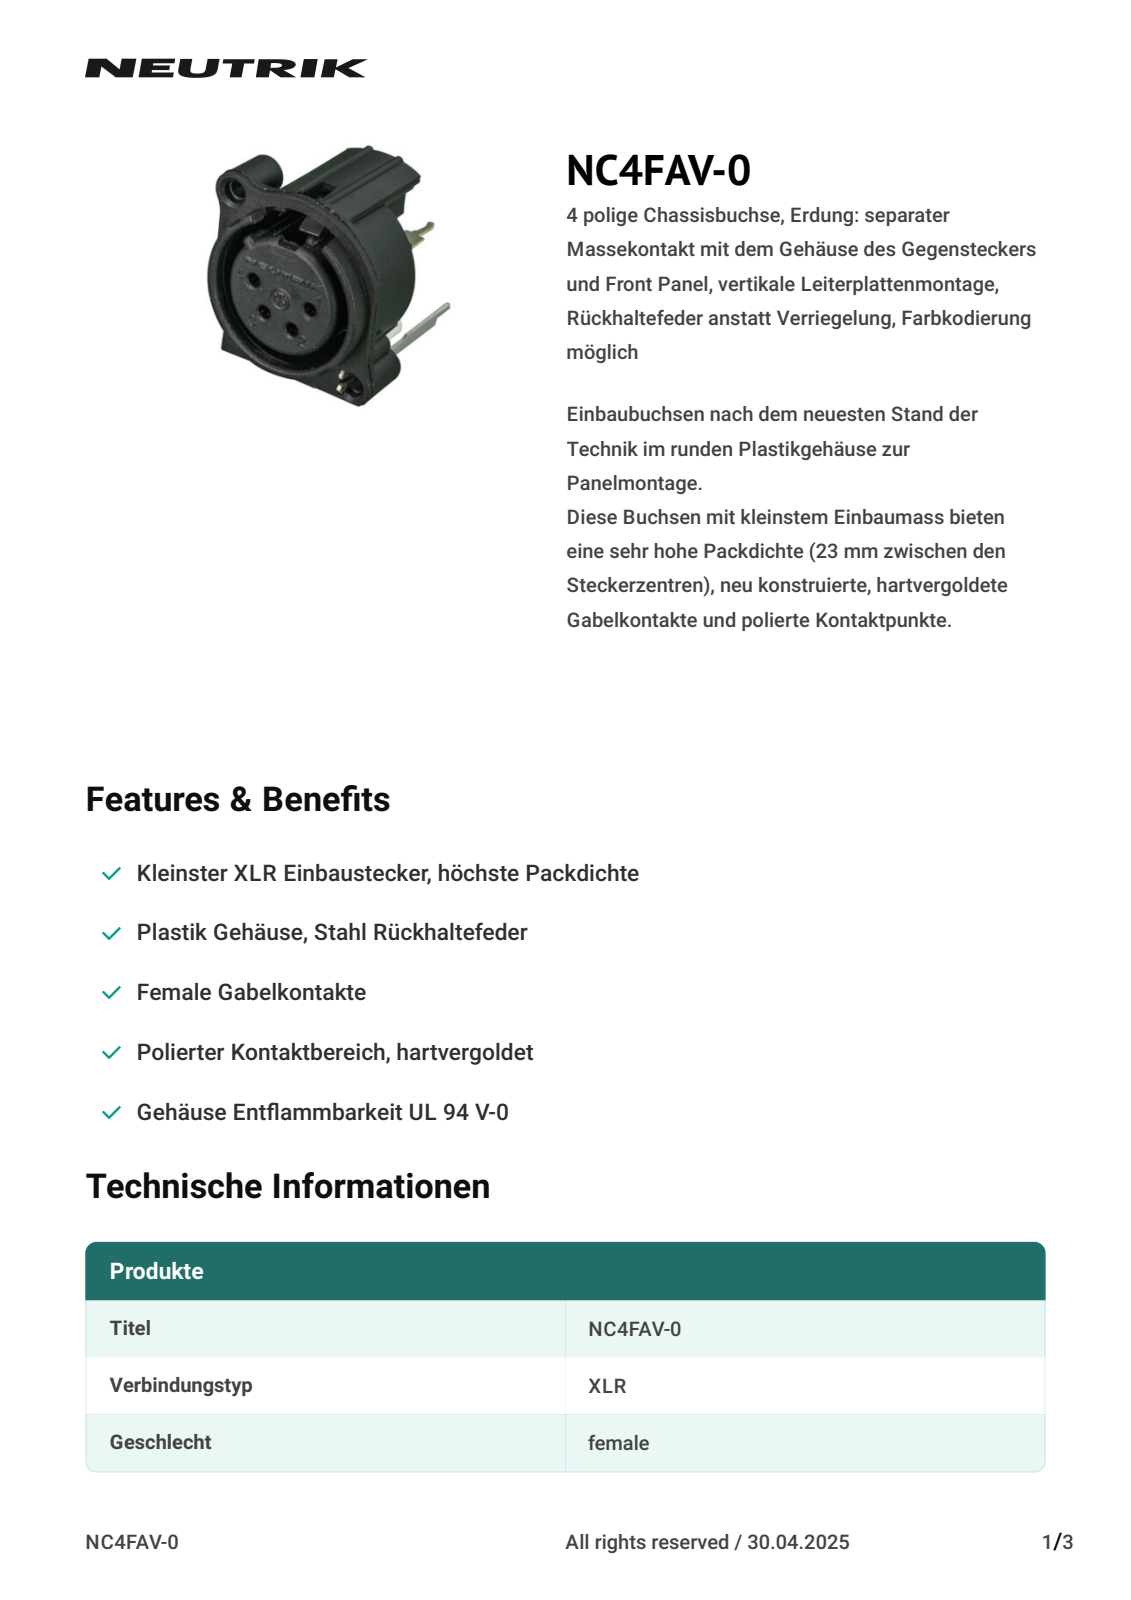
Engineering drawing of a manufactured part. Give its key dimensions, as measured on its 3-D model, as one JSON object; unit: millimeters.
{"part_name": "NC4FAV-0", "step_written_by": "CREO PARAMETRIC BY PTC INC, 2018360 (CONFIG_CONTROL_DESIGN)", "units": "millimeters", "bodies": {"solids": 1, "faces": 1107, "planar": 743, "cylindrical": 255, "other": 109}, "overall_size": [31.02, 26.5, 25], "volume_mm3": 4903, "surface_area_mm2": 6882, "round_holes": [[1.7, 4], [2.35, 2], [1.27, 1], [1.4, 1], [2.5, 1], [3, 1], [19.5, 1], [20.5, 1]], "round_bosses_or_shafts": [[1.5, 2], [22, 1], [15.8, 1], [5.2, 1], [3, 1]], "partial_cylinders_radius": [[0.2, 85], [0.5, 30], [0.12, 9], [1, 4], [0.75, 3], [1.5, 3], [2.12, 3], [5, 3]], "face_to_face_distances": [0.5, 1, 11.8, 2.7, 0.94, 2.84, 3.78, 2, 14.5, 5.6], "hole_center_spacings": [3.22, 4.27, 11.62, 14, 25.53, 3.55, 4.19, 4.2]}
